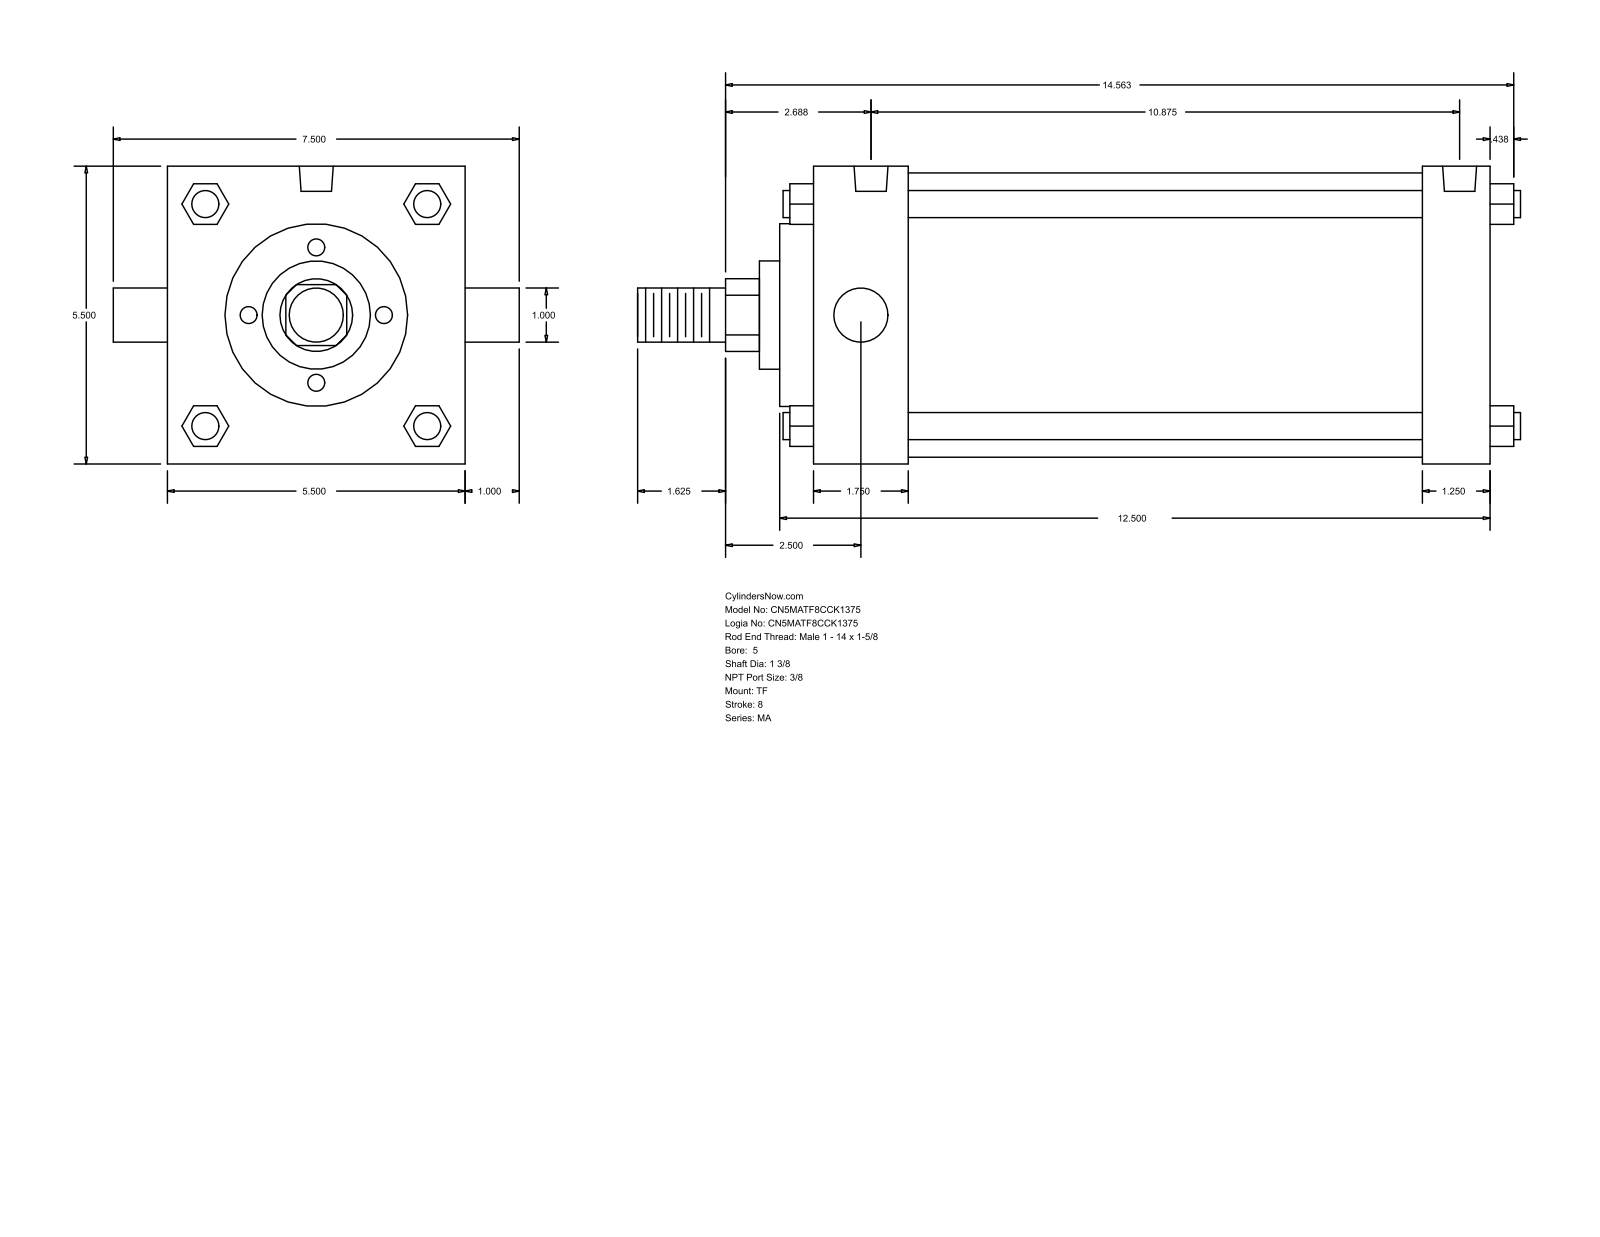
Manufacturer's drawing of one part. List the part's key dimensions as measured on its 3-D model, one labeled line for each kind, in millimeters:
Part name (STEP PRODUCT): MA_TF__0500_1.375
STEP written by: GSSL Pune (CONFIG_CONTROL_DESIGN)
Units: millimetres
Bodies: 0 solids, 122 faces (93 planar, 29 cylindrical, 0 other)
Overall size (bounding box): 414.34 × 190.5 × 139.7
Round holes (diameter × count): ⌀11.11 ×3, ⌀15.93 ×2
Round bosses / shafts (diameter × count): ⌀12.7 ×4, ⌀25.4 ×2, ⌀133.35 ×1, ⌀85.72 ×1, ⌀50.8 ×1, ⌀34.92 ×1
Partial cylindrical surfaces — rounded edges, fillets, slot ends (radius × count): R17.06 ×1
Main face-to-face distances: 139.7, 317.5, 285.75, 31.75, 44.45, 241.3, 273.05, 15.87, 60.32, 301.62
Hole centre spacings: 4.76, 4.77, 266.7, 271.46, 271.47, 276.23
